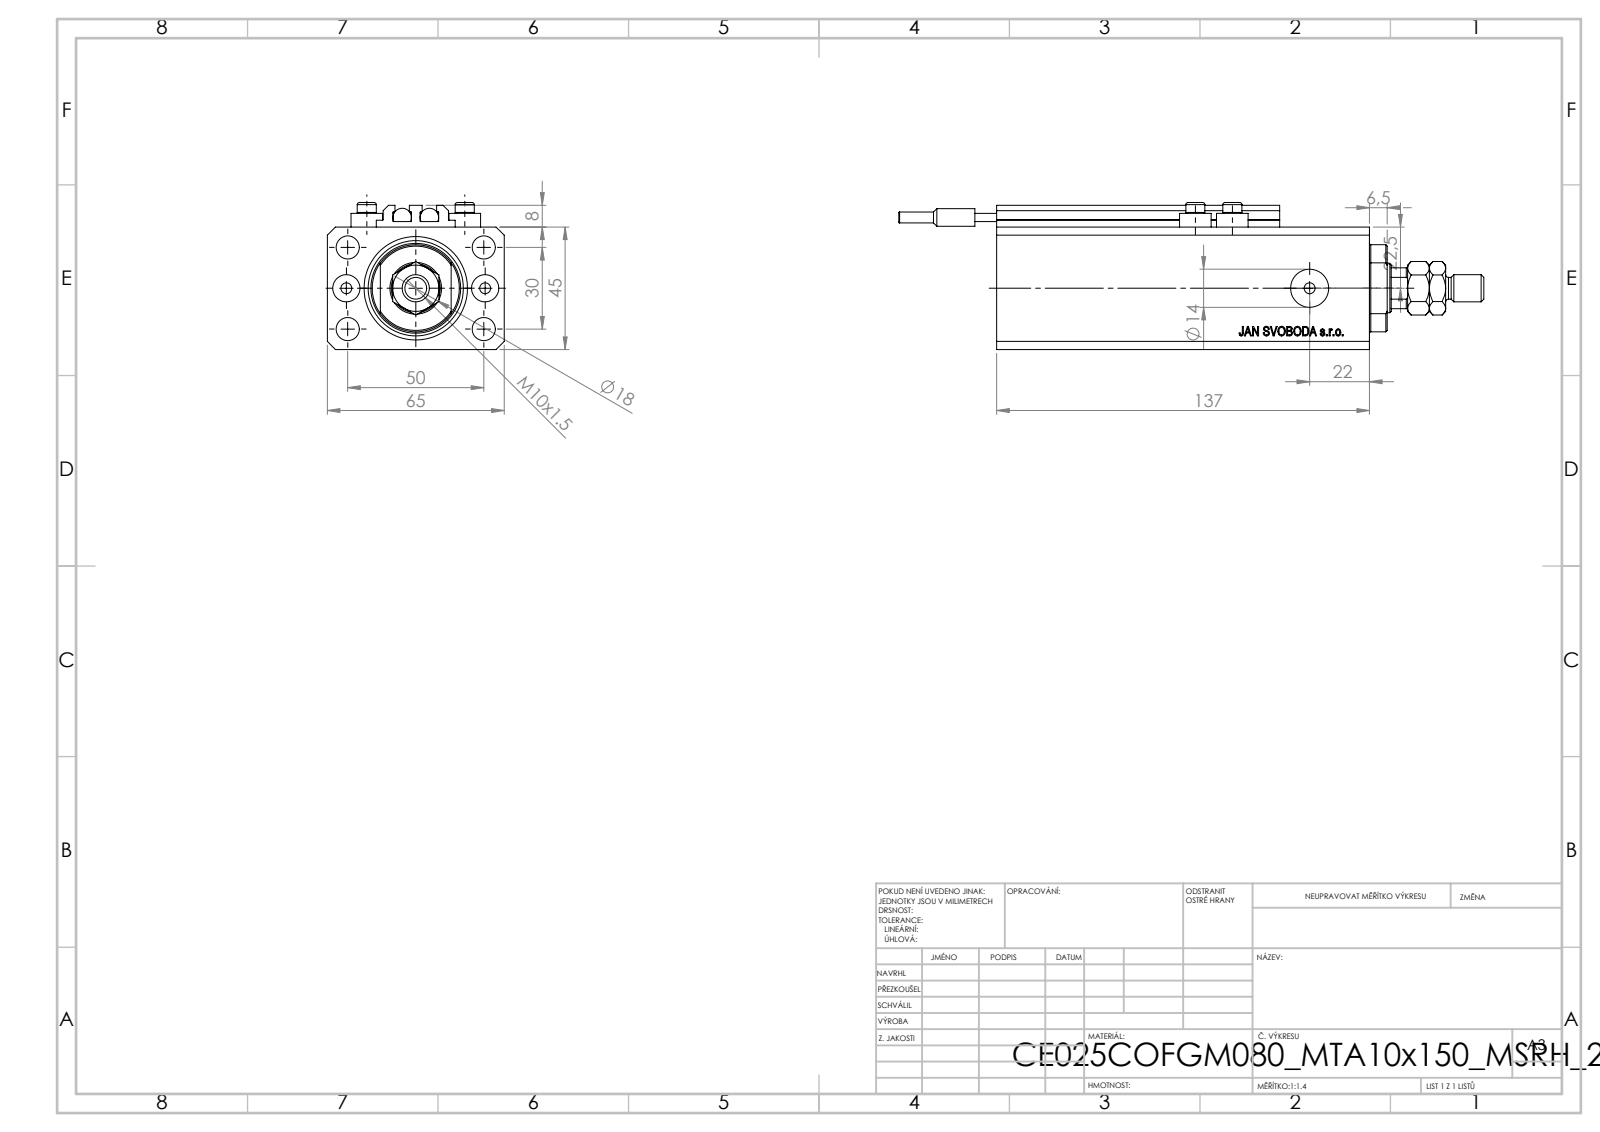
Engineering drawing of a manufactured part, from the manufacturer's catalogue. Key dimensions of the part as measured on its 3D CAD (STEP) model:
Part name (STEP PRODUCT): V250CE_VC_C; V250CE_C_VCP; SWITCH_V250CE; MTA (+2 more)
STEP written by: SolidWorks 2019 (CONFIG_CONTROL_DESIGN)
Units: millimetres
Bodies: 11 solids, 1135 faces (551 planar, 102 cylindrical, 482 other)
Overall size (bounding box): 215 × 65 × 54
Volume: 374 186 mm³ · Surface area: 95 094 mm²
Round holes (diameter × count): ⌀4 ×8, ⌀8.5 ×5, ⌀10 ×2, ⌀14 ×2, ⌀18 ×1, ⌀25 ×1, ⌀38 ×1
Round bosses / shafts (diameter × count): ⌀11.6 ×4, ⌀7 ×4, ⌀6.8 ×2, ⌀6.5 ×2, ⌀4 ×2, ⌀10 ×1, ⌀8 ×1
Partial cylindrical surfaces — rounded edges, fillets, slot ends (radius × count): R0.2 ×10, R8.5 ×1, R16 ×1
Main face-to-face distances: 45, 65, 14, 47, 2, 123, 2.5, 3, 137, 10
Hole centre spacings: 15.01, 29.15, 52.68, 13.6, 25.5, 30, 36, 38.48
